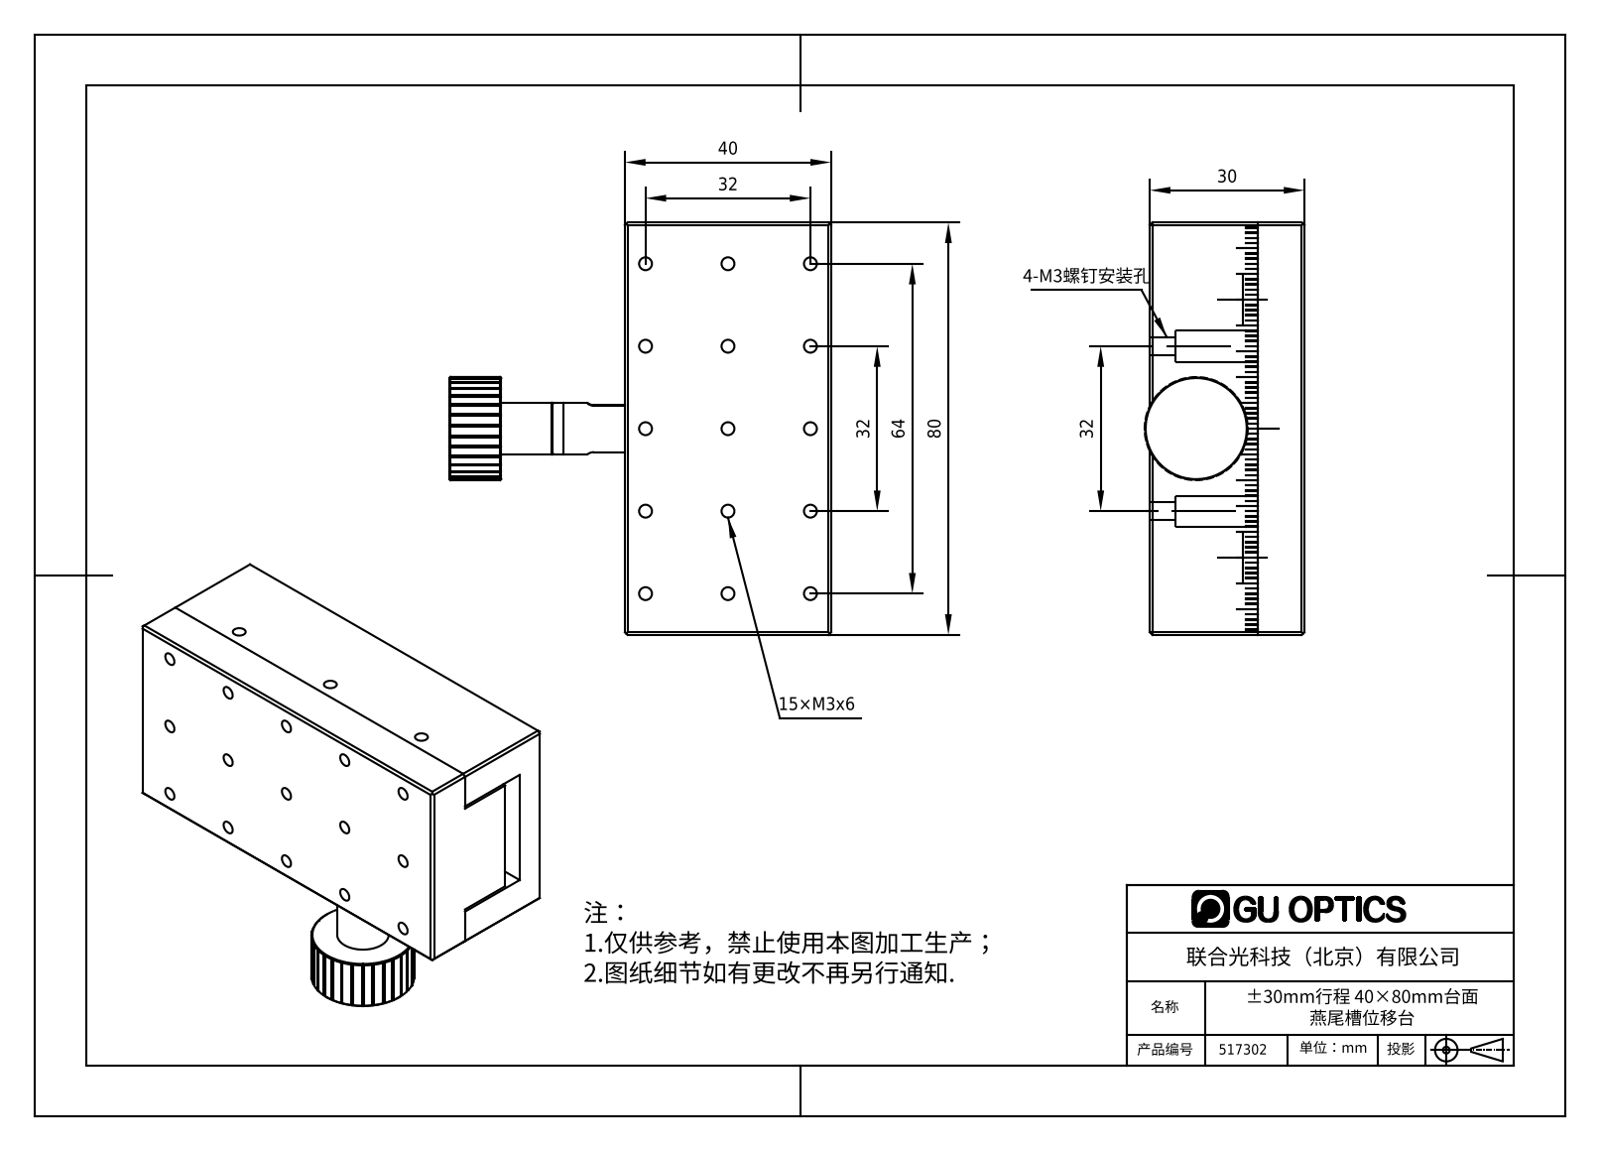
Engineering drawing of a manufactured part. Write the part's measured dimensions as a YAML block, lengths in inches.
part_name: "517302"
step_written_by: "SolidWorks 2016 (AUTOMOTIVE_DESIGN)"
units: inches
bodies: {solids: 7, faces: 647, planar: 445, cylindrical: 123, other: 79}
overall_size: [3.15, 2.913, 1.22]
volume: 5.394
surface_area: 46.08
round_holes:
  - {diameter: 0.098, count: 19}
  - {diameter: 0.138, count: 4}
  - {diameter: 0.236, count: 4}
  - {diameter: 0.177, count: 3}
  - {diameter: 0.315, count: 2}
  - {diameter: 0.13, count: 1}
round_bosses_or_shafts:
  - {diameter: 0.098, count: 2}
  - {diameter: 0.787, count: 1}
  - {diameter: 0.394, count: 1}
  - {diameter: 0.335, count: 1}
  - {diameter: 0.315, count: 1}
partial_cylinders:
  - {radius: 0.079, count: 2}
face_to_face_distances: [1.181, 0.295, 1.28, 0.827, 0.354, 0.394, 1.575, 0.945, 0.787, 0.433]
hole_center_spacings: [0.63, 1.409, 0.891, 1.26, 1.992, 1.781, 1.89, 0.645]
